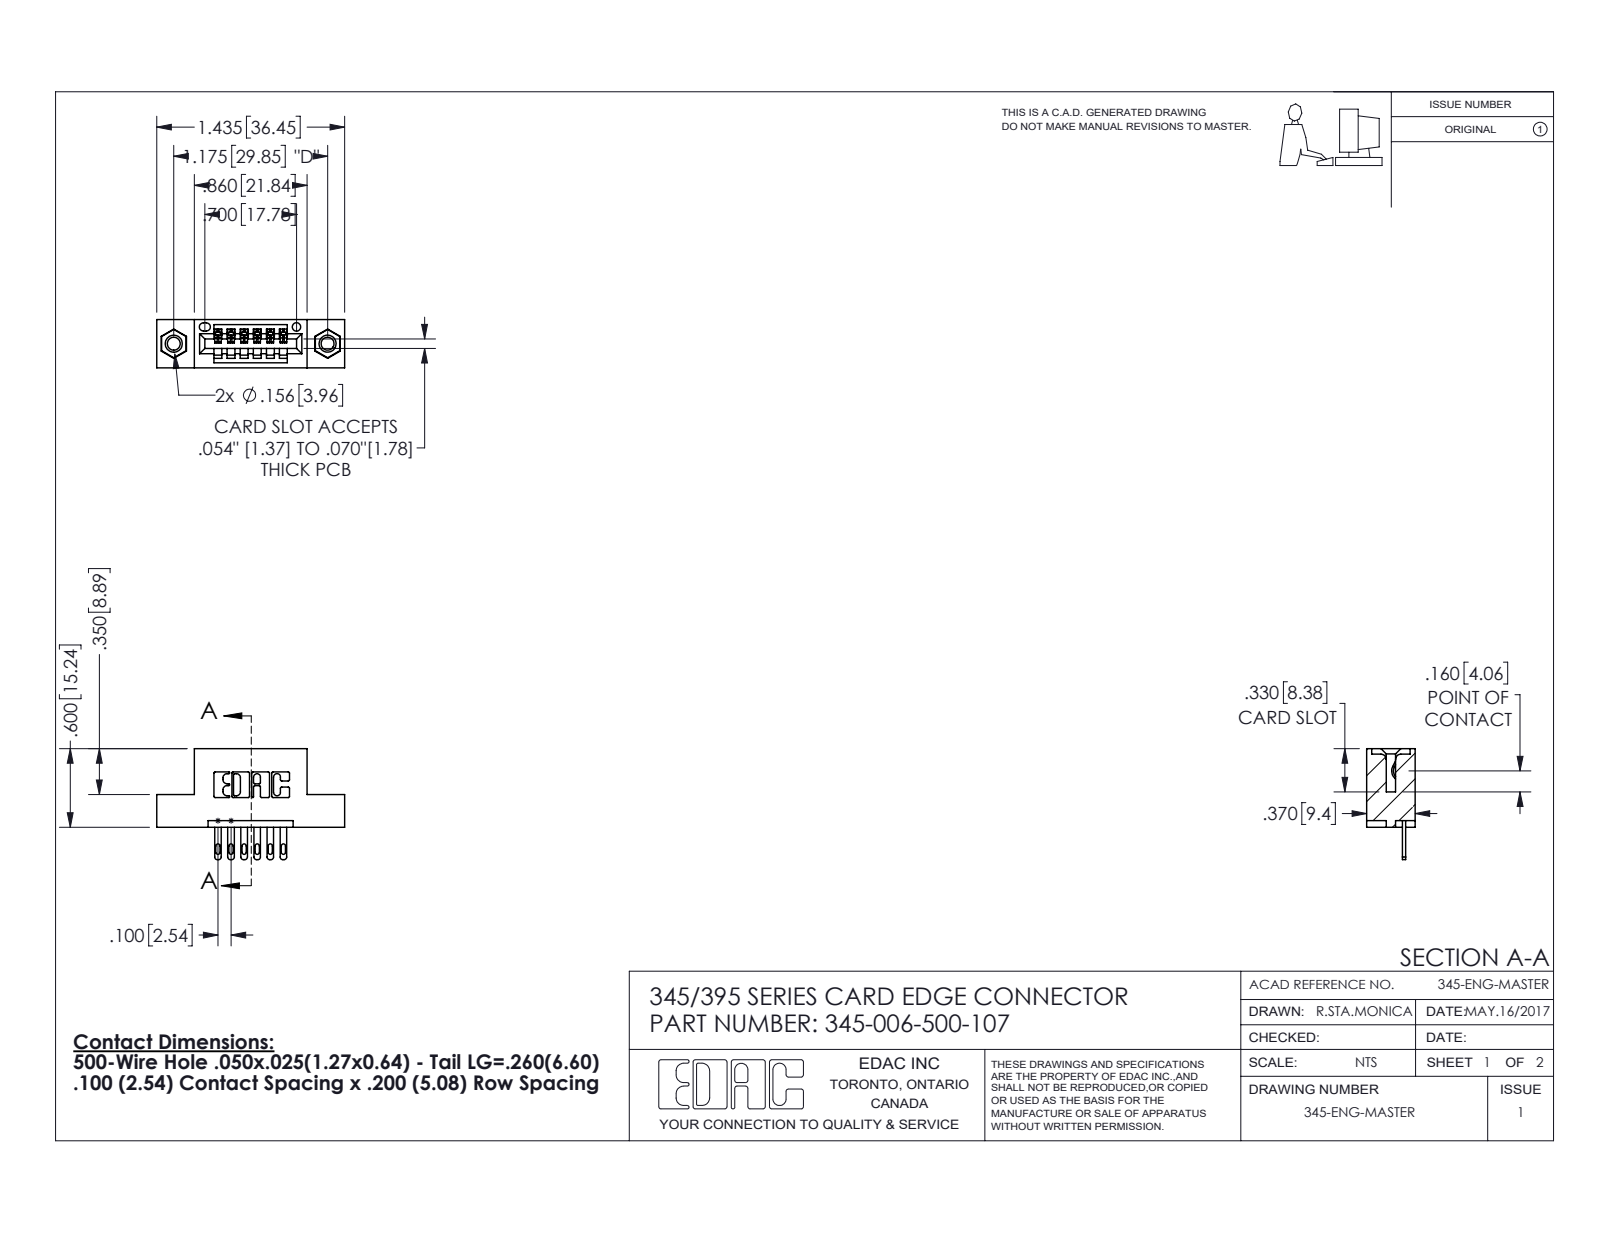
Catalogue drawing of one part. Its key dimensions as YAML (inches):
part_name: "345-292-001_345-293-100; 345 Part_Flush Mounting Lugs - 0.156 Dia-TI; 345-006-500-107; 345-250-001_345-250-005-103"
step_written_by: "SolidWorks 2016 (CONFIG_CONTROL_DESIGN)"
units: inches
bodies: {solids: 9, faces: 510, planar: 316, cylindrical: 178, other: 16}
overall_size: [1.435, 0.847, 0.37]
volume: 0.193
surface_area: 5.816
round_holes:
  - {diameter: 0.098, count: 2}
  - {diameter: 0.125, count: 2}
  - {diameter: 0.156, count: 2}
  - {diameter: 0.064, count: 1}
round_bosses_or_shafts:
  - {diameter: 0.155, count: 2}
partial_cylinders:
  - {radius: 0.01, count: 22}
  - {radius: 0.006, count: 12}
  - {radius: 0.016, count: 12}
  - {radius: 0.02, count: 12}
  - {radius: 0.007, count: 6}
  - {radius: 0.031, count: 6}
  - {radius: 0.026, count: 3}
  - {radius: 0.031, count: 2}
face_to_face_distances: [0.2, 0.37, 0.072, 0.298, 0.1, 0.098, 0.272, 0.025, 0.06, 0.3]
hole_center_spacings: [0.27, 0.946, 1.175]
